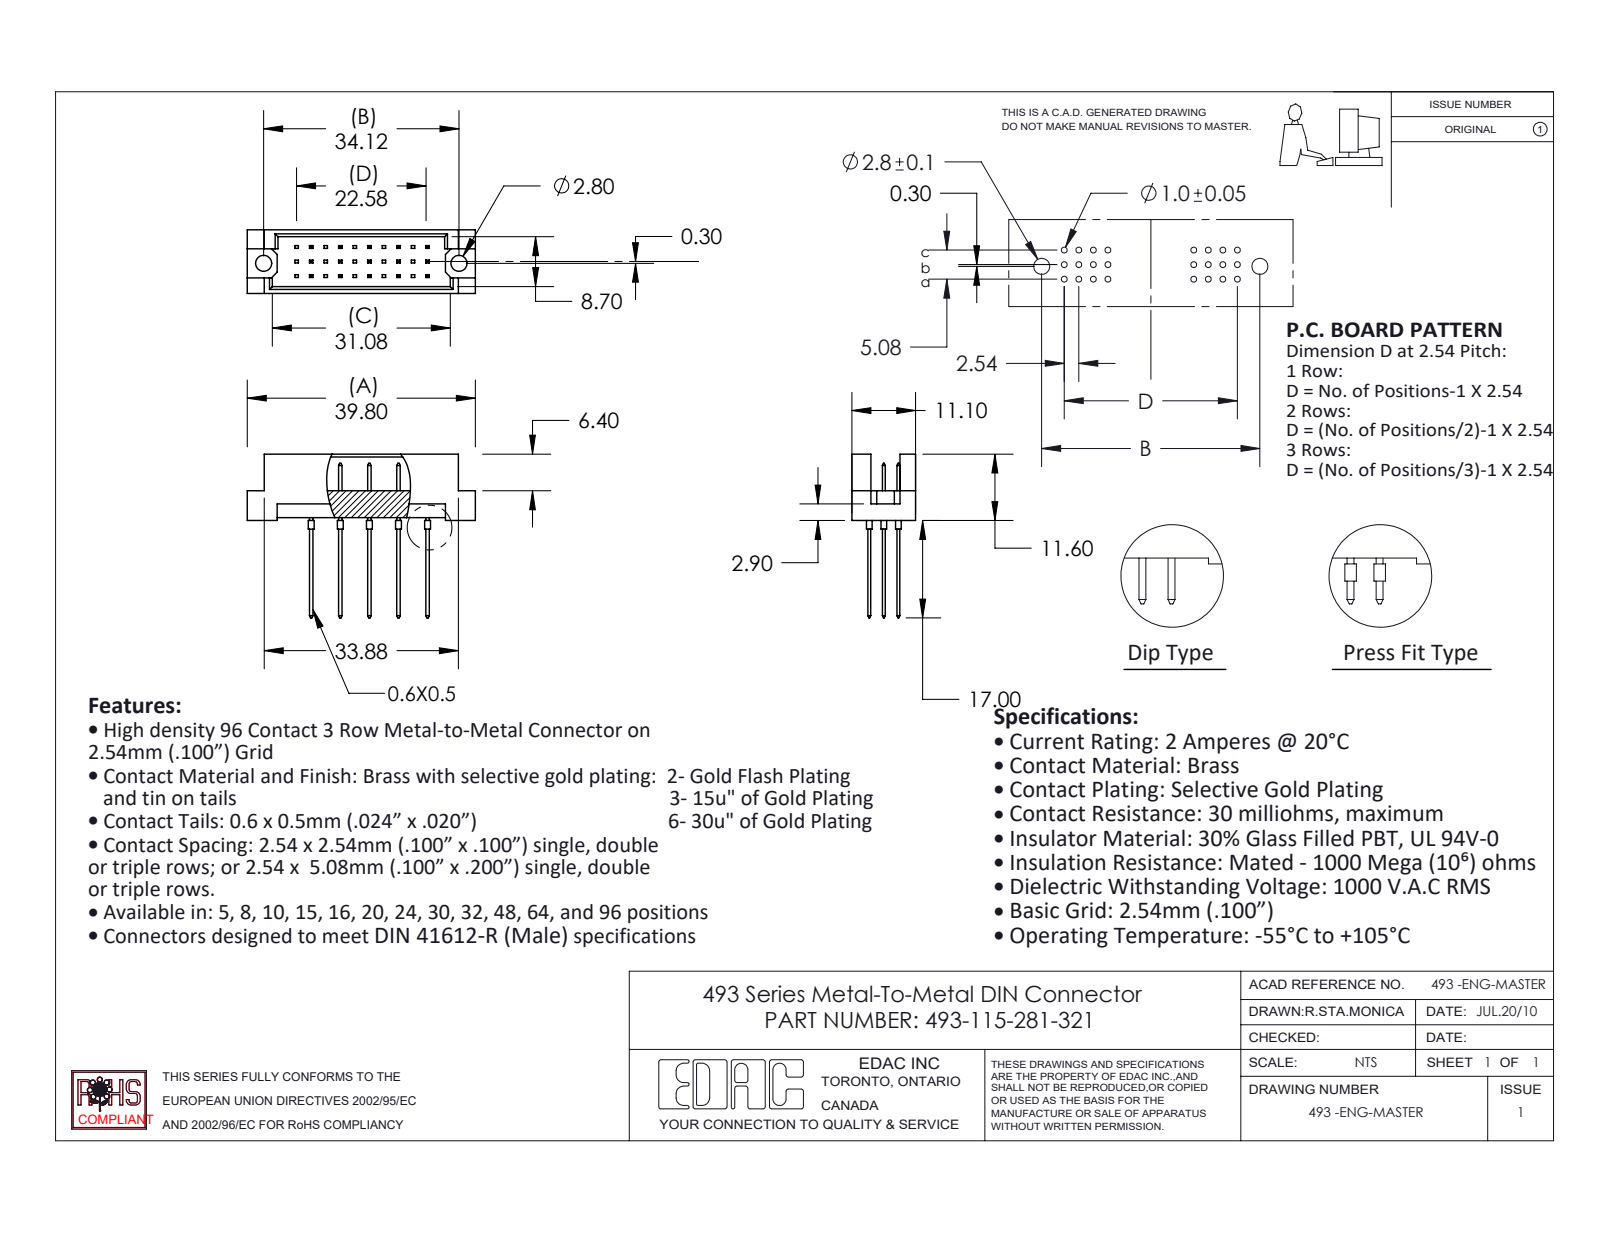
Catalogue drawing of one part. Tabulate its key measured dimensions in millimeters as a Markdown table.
| quantity | value |
| --- | --- |
| part name | 493 Part_30; 493-290_81; 493-115-281-321 |
| STEP written by | SolidWorks 2020 (CONFIG_CONTROL_DESIGN) |
| units | millimeters |
| bodies | 16 solids, 502 faces (468 planar, 34 cylindrical, 0 other) |
| overall size | 39.8 × 28.6 × 11.1 |
| volume | 2 504 mm³ |
| surface area | 3 659 mm² |
| round holes (diameter × count) | 2.8 × 2 |
| round bosses / shafts (diameter × count) | 1 × 15 |
| main face-to-face distances | 5.08, 1.2, 9.9, 0.5, 2.54, 11.1, 8.7, 10.16, 4.7, 0.6 |
| hole center spacings | 34.12 |
